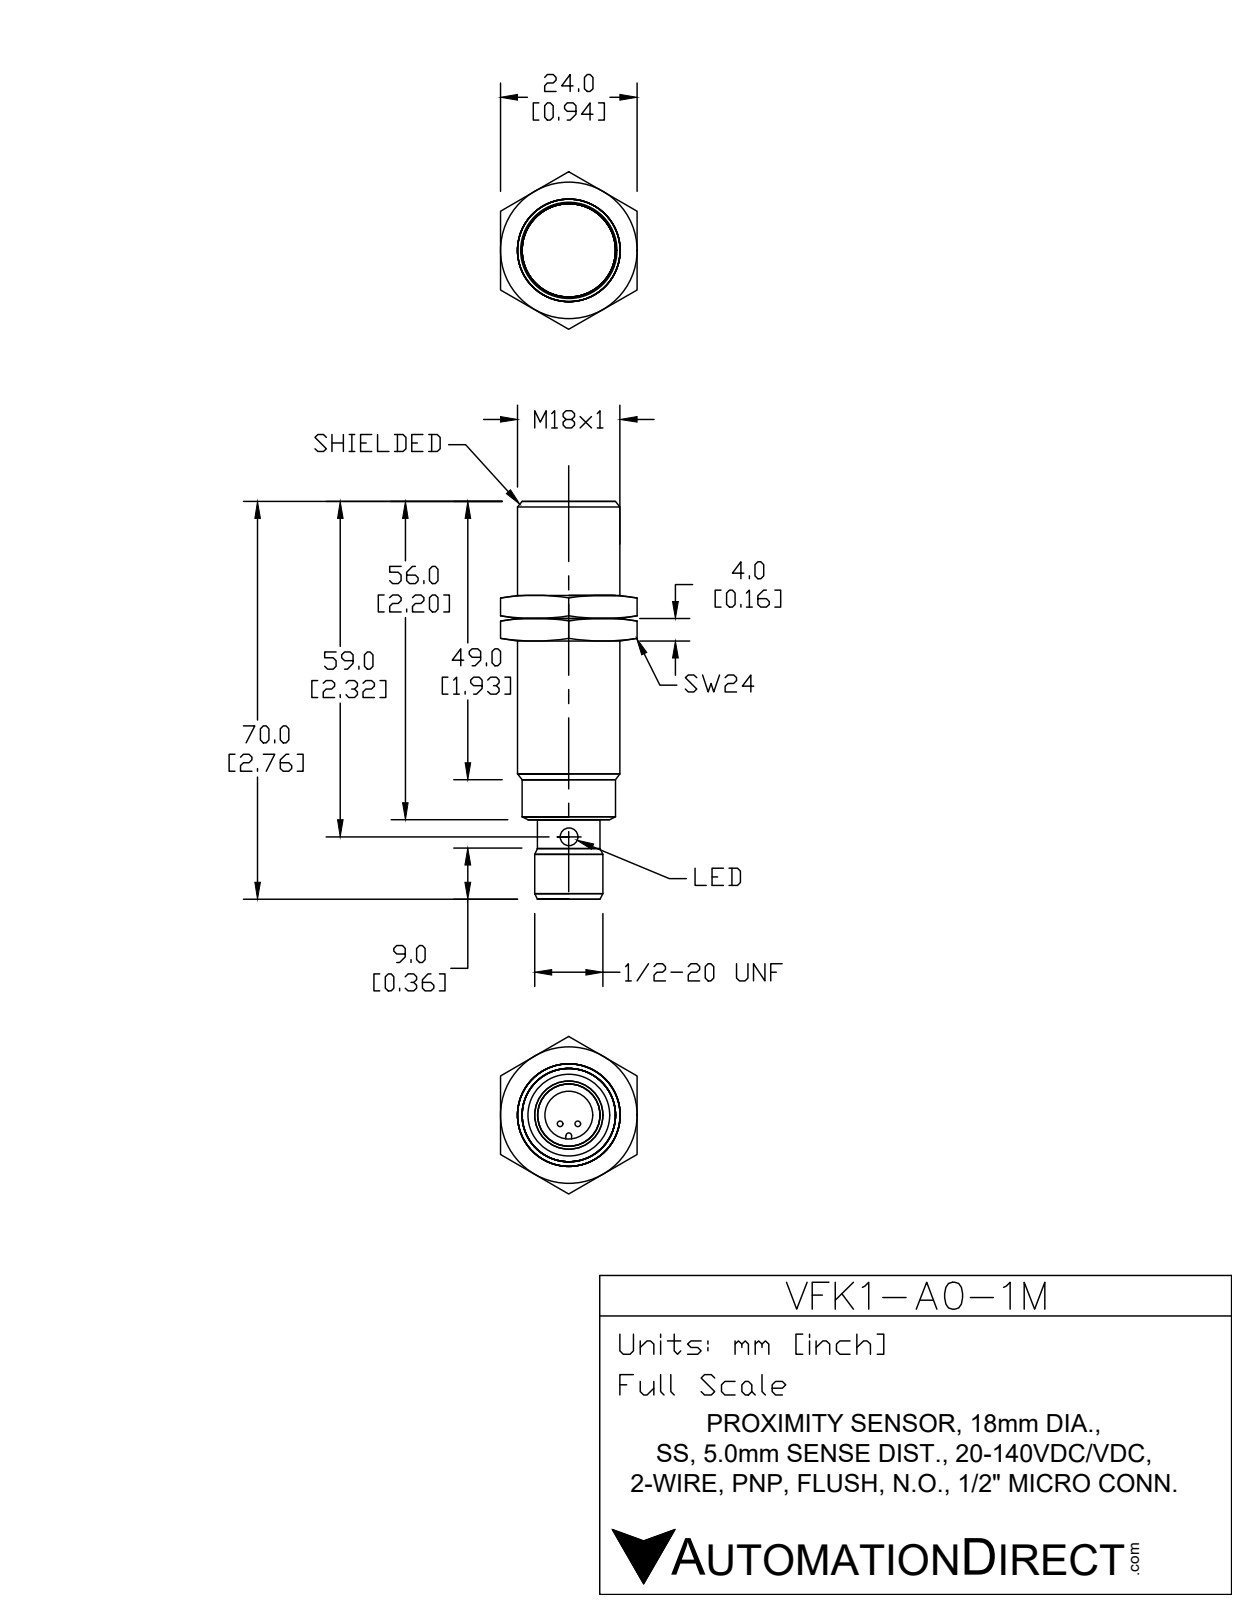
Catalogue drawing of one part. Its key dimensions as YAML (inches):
part_name: "VFK1-A0-1M"
step_written_by: "SolidWorks 2017 (AUTOMOTIVE_DESIGN)"
units: inches
bodies: {solids: 3, faces: 119, planar: 27, cylindrical: 44, other: 48}
overall_size: [2.756, 1.091, 0.945]
volume: 1.061
surface_area: 9.915
round_holes:
  - {diameter: 0.098, count: 1}
  - {diameter: 0.118, count: 1}
  - {diameter: 0.299, count: 1}
  - {diameter: 0.666, count: 1}
round_bosses_or_shafts:
  - {diameter: 0.709, count: 1}
  - {diameter: 0.654, count: 1}
  - {diameter: 0.63, count: 1}
  - {diameter: 0.5, count: 1}
  - {diameter: 0.445, count: 1}
  - {diameter: 0.417, count: 1}
partial_cylinders:
  - {radius: 0.008, count: 8}
  - {radius: 0.173, count: 1}
  - {radius: 0.197, count: 1}
face_to_face_distances: [0.157, 0.945, 0.984, 0.827, 0.315, 1.142, 1.102, 1.26, 1.417, 2.244]
